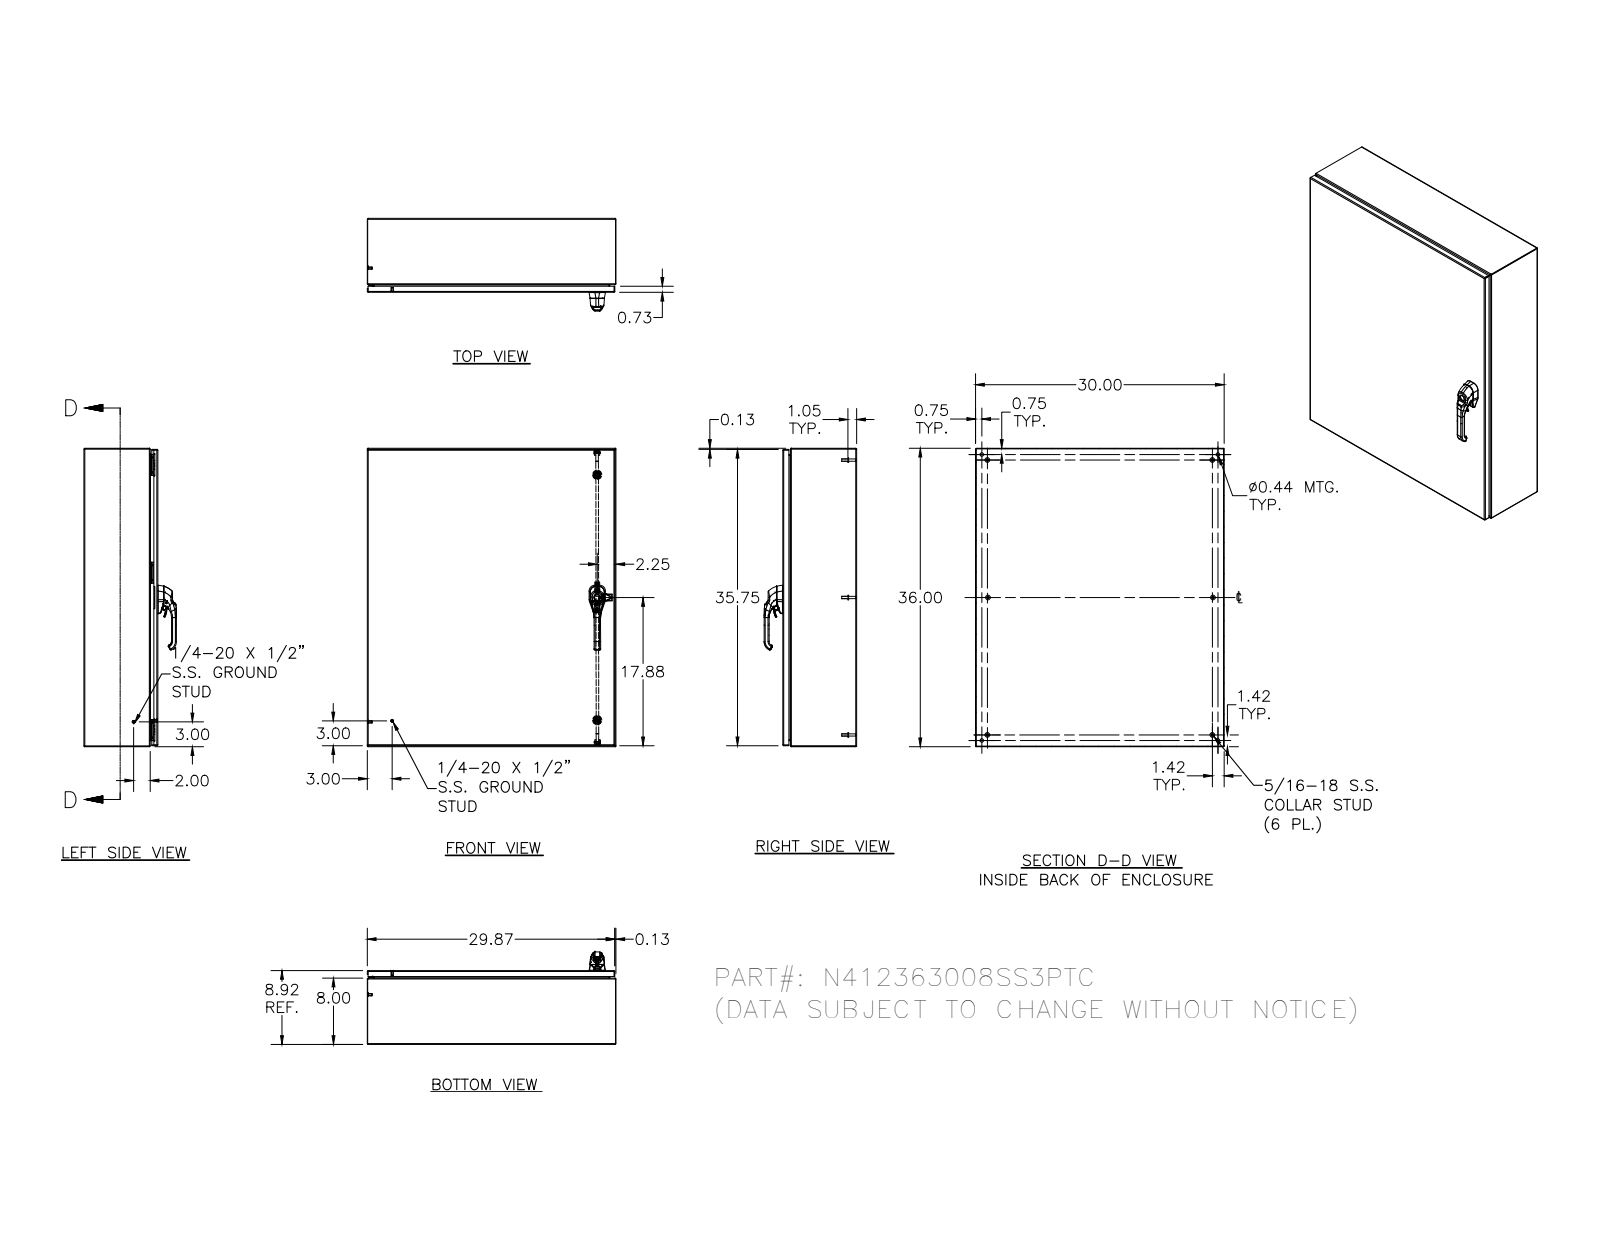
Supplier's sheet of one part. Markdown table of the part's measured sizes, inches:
| quantity | value |
| --- | --- |
| part name | N412363008SS3PTC; N412363008SS3PTCBKP; N4123630SS3PTCLID; HFW328176 (+8 more) |
| STEP written by | Autodesk Inventor 2011 (AUTOMOTIVE_DESIGN) |
| units | inches |
| bodies | 74 solids, 3522 faces (1171 planar, 1295 cylindrical, 1056 other) |
| overall size | 36 × 30 × 11.166 |
| volume | 269.2 in³ |
| surface area | 7 149 in² |
| round holes (diameter × count) | 0.093 × 6, 0.152 × 6, 0.165 × 6, 0.167 × 6, 0.172 × 6, 0.188 × 6, 0.197 × 4, 0.437 × 4, 0.156 × 3, 0.213 × 3, 0.106 × 2, 0.16 × 2 |
| round bosses / shafts (diameter × count) | 0.25 × 14, 0.591 × 6, 0.563 × 6, 0.36 × 6, 0.32 × 6, 0.3 × 6, 0.275 × 6, 0.256 × 6 |
| partial cylindrical surfaces (radius × count) | 0.02 × 186, 0.012 × 100, 0.05 × 38, 0.031 × 34, 0.016 × 26, 0.019 × 23, 0.118 × 23, 0.125 × 21 |
| main face-to-face distances | 0.074, 8.843, 8.769, 8.917, 29.926, 35.926, 29.852, 30, 36, 35.852 |
| hole center spacings | 13, 31.996, 18.996, 0.017, 0.66, 32, 0.019, 0.5 |
